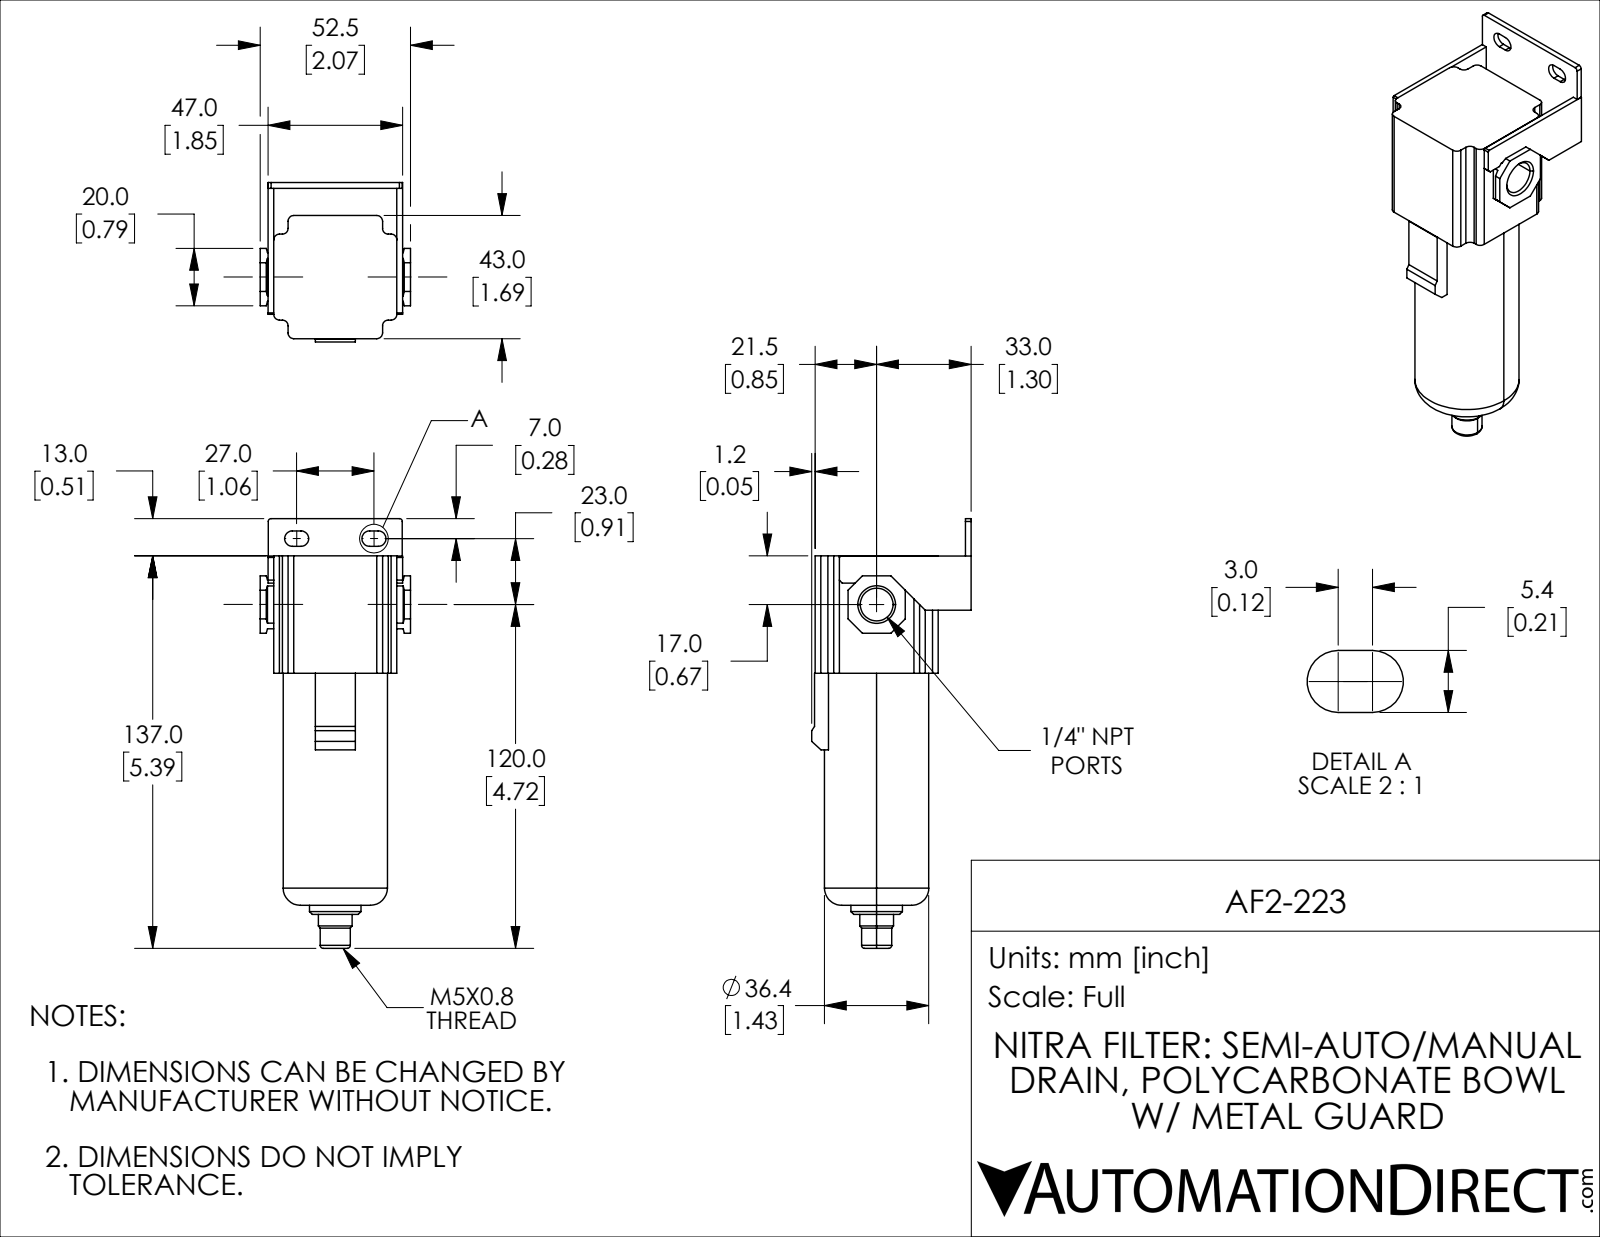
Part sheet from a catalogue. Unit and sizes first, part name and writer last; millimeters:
Units: millimetres
Overall size (bounding box): 150 × 55.67 × 52.5
Round holes (diameter × count): ⌀4.13 ×1, ⌀11.45 ×1
Round bosses / shafts (diameter × count): ⌀36.4 ×1, ⌀18 ×1, ⌀11.8 ×1, ⌀10.5 ×1
Partial cylindrical surfaces — rounded edges, fillets, slot ends (radius × count): R2 ×12, R2.7 ×4, R1 ×2
Main face-to-face distances: 2, 43, 9.5, 52.5, 11.5, 45, 54.5, 41, 47, 5
Volume: 162 539 mm³ · Surface area: 26 433 mm²
Bodies: 1 solid, 136 faces (90 planar, 32 cylindrical, 14 other)
Part name (STEP PRODUCT): AF2-223
STEP written by: SolidWorks 2019 (CONFIG_CONTROL_DESIGN)
